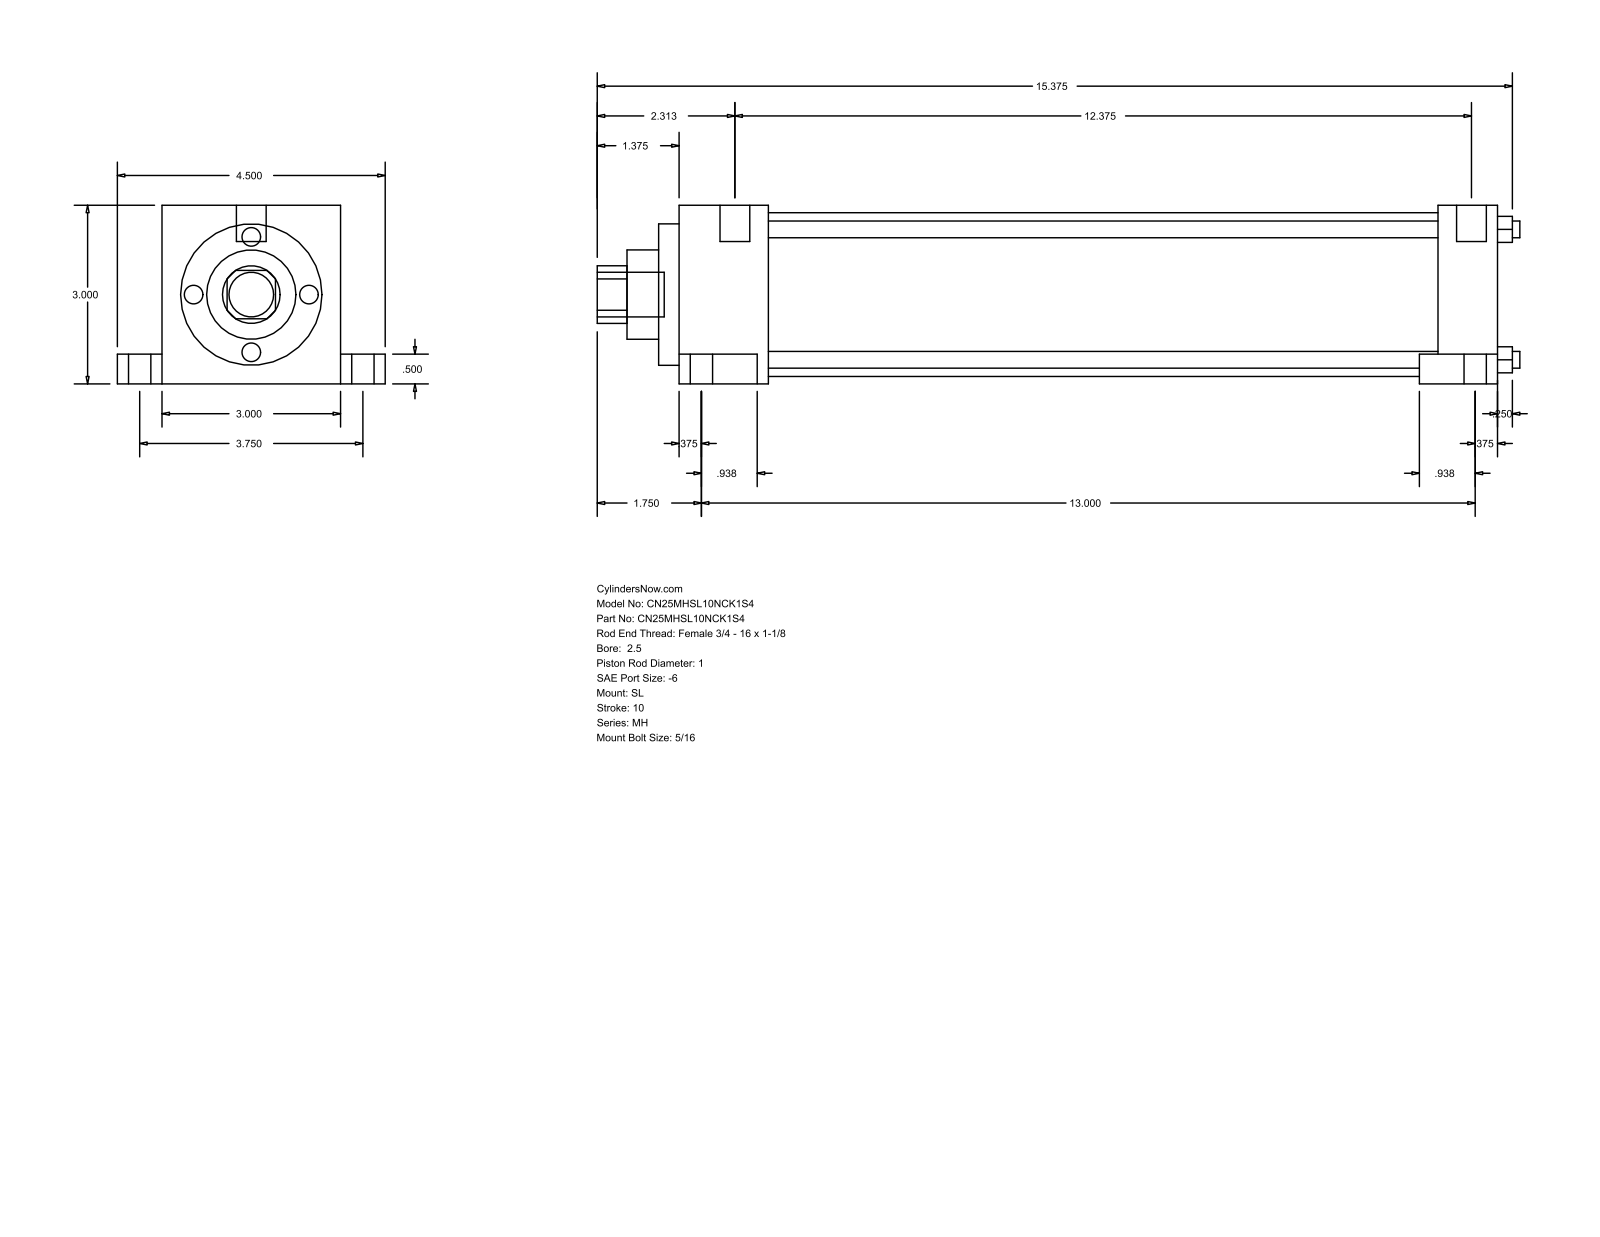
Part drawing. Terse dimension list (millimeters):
name: MH_SL__0250_1
written by: GSSL Pune (CONFIG_CONTROL_DESIGN)
unit: mm
bodies: 0 solids, 86 faces (61 planar, 25 cylindrical, 0 other)
size: 393.7 × 114.3 × 76.2
holes: 4× ⌀7.14, 1× ⌀25.4, 1× ⌀38.1, 1× ⌀60.33, 1× ⌀69.85
bosses: 2× ⌀15.88, 2× ⌀9.53, 2× ⌀5.56, 1× ⌀19.05, 1× ⌀12.7
rounds: 1× R12.29
face distances: 76.2, 25.41, 332.58, 357.99, 12.7, 63.5, 19.05, 95.25, 13.49, 346.07
hole spacings: 39.33, 55.62, 78.66
